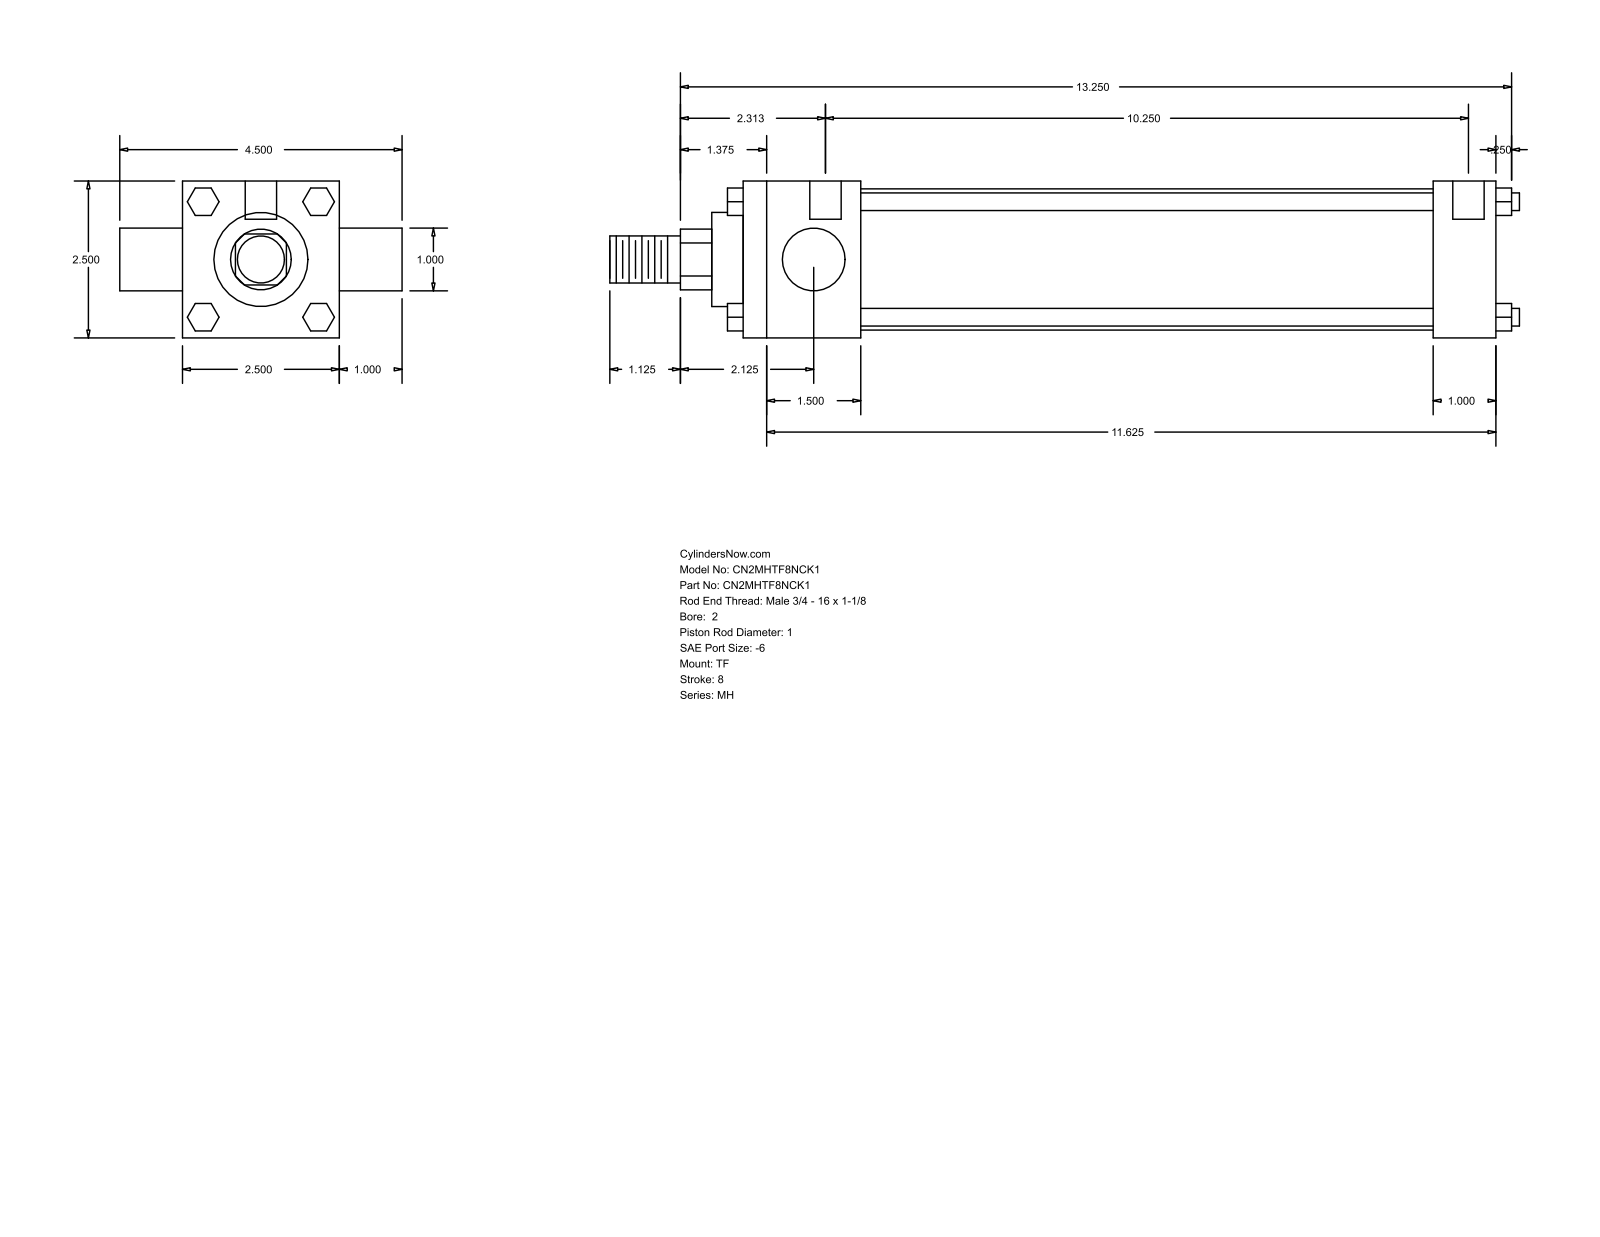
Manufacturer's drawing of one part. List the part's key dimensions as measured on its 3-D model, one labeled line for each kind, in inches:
Part name (STEP PRODUCT): MH_TF__0200_1
STEP written by: GSSL Pune (CONFIG_CONTROL_DESIGN)
Units: inches
Bodies: 0 solids, 120 faces (92 planar, 28 cylindrical, 0 other)
Overall size (bounding box): 14.5 × 4.5 × 2.5
Round holes (diameter × count): ⌀0.219 ×3, ⌀0.5 ×2
Round bosses / shafts (diameter × count): ⌀0.281 ×4, ⌀1 ×2, ⌀2.25 ×1, ⌀1.5 ×1, ⌀0.75 ×1
Partial cylindrical surfaces — rounded edges, fillets, slot ends (radius × count): R0.484 ×1
Main face-to-face distances: 2.5, 12, 1, 1.875, 11, 9.125, 10.125, 3.5, 12.5, 0.25
Hole centre spacings: 0.125, 0.187, 10.25, 10.375, 10.437, 10.562
